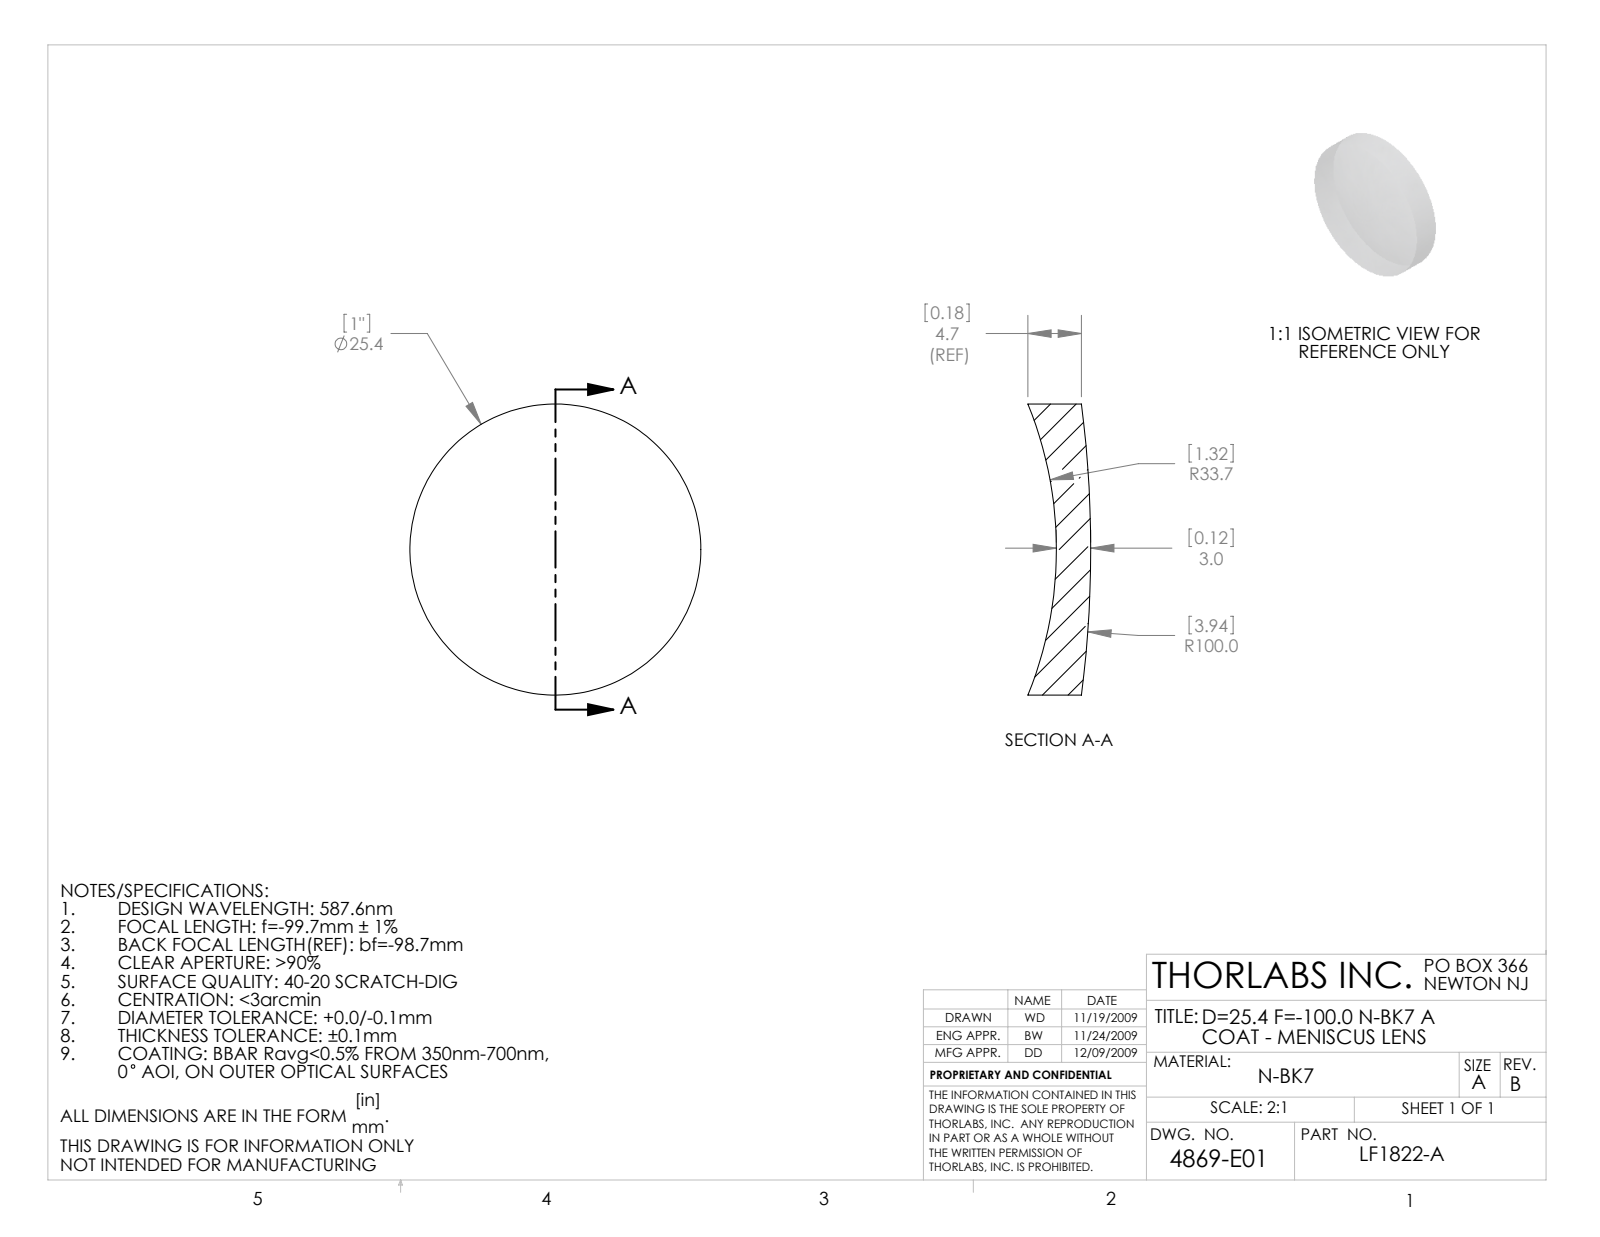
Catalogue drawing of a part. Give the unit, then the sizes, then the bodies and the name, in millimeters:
Units: millimetres
Overall size (bounding box): 25.4 × 25.4 × 5.49
Round bosses / shafts (diameter × count): ⌀25.4 ×1
Volume: 1 938 mm³ · Surface area: 1 408 mm²
Bodies: 1 solid, 6 faces (0 planar, 2 cylindrical, 4 other)
Part name (STEP PRODUCT): 4869-E0W
STEP written by: SolidWorks 2009 (AUTOMOTIVE_DESIGN)
